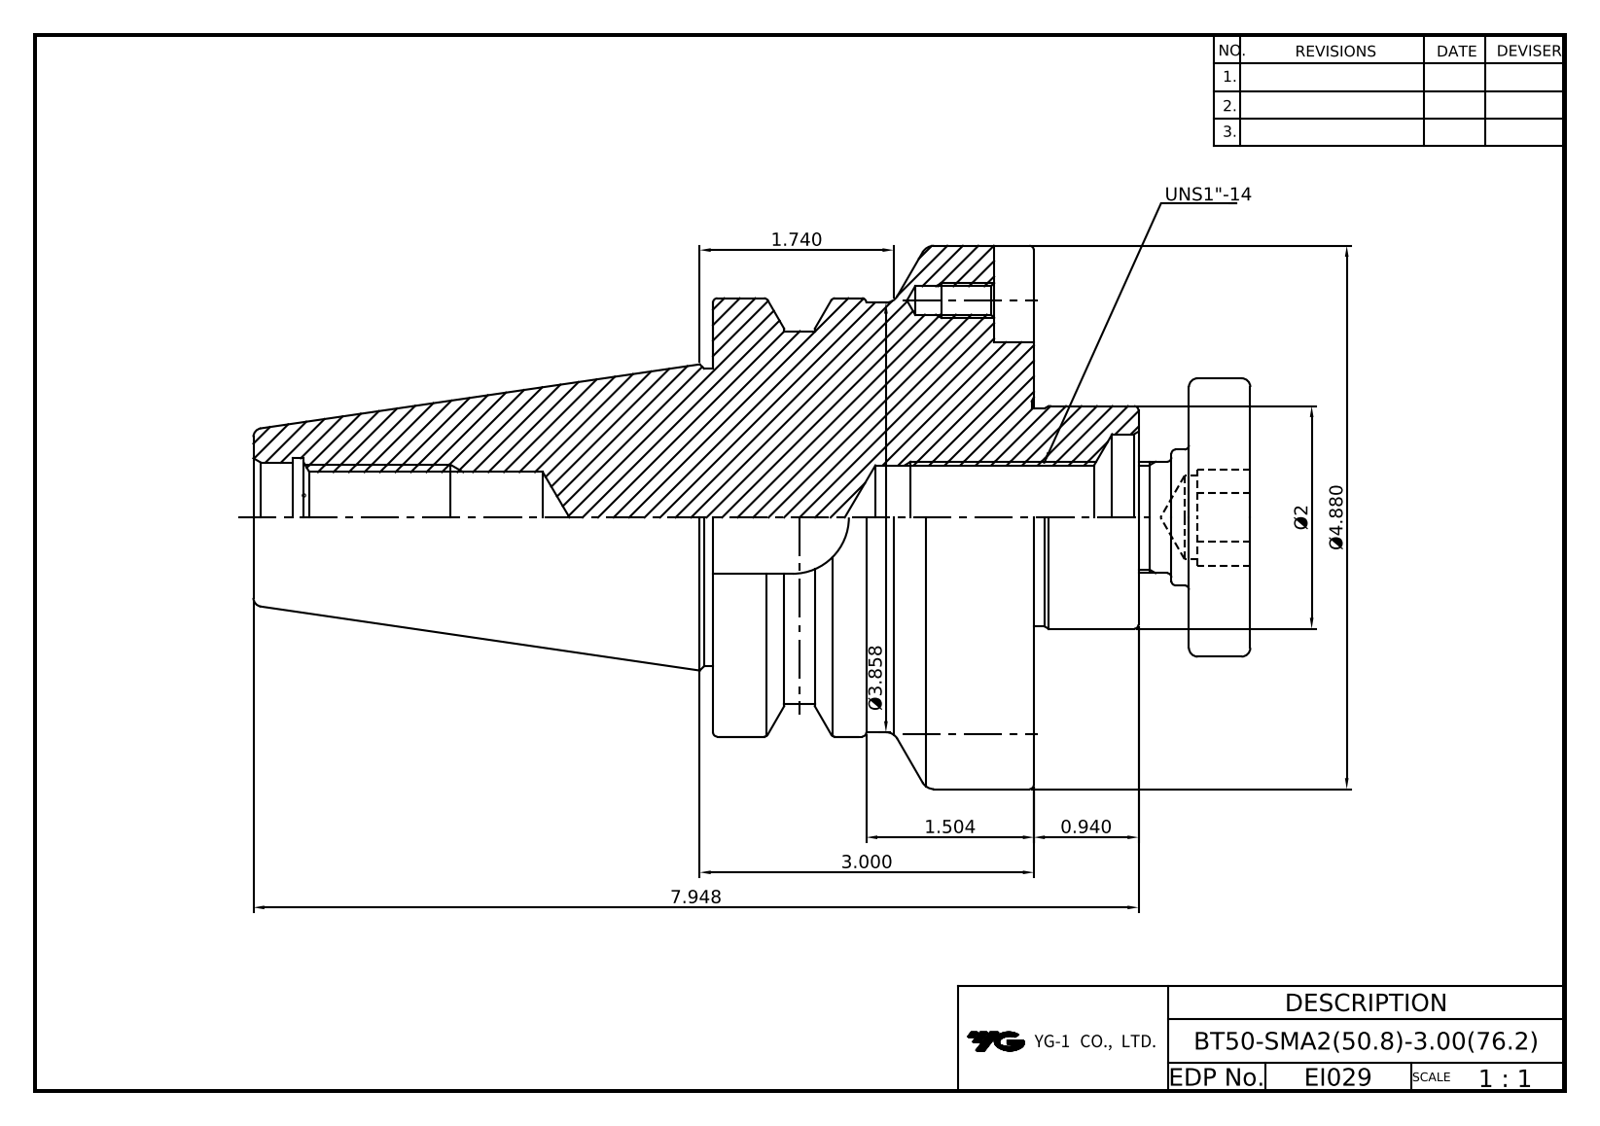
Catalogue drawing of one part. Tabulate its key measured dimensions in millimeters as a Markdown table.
| quantity | value |
| --- | --- |
| part name | LO-BT50-SMA50.8-76.2; DRIVE KEY-19.05.x18x22; HEX'' WRENCH BOLT-UNC5_16-18x3_4L; COLLAR BOLT-UNS1-14x50L |
| STEP written by | Autodesk Inventor 2026 (AUTOMOTIVE_DESIGN) |
| units | millimeters |
| bodies | 6 solids, 142 faces (68 planar, 35 cylindrical, 39 other) |
| overall size | 223.3 × 124 × 124 |
| volume | 948 500 mm³ |
| surface area | 105 500 mm² |
| round holes (diameter × count) | 6.4 × 2, 8.6 × 2, 12.6 × 2, 19.1 × 1, 20.5 × 1, 20.8 × 1, 23.4 × 1, 25 × 1, 25.6 × 1, 38 × 1 |
| round bosses / shafts (diameter × count) | 11.9 × 2, 7.9 × 2, 124 × 1, 100 × 1, 98 × 1, 84.6 × 1, 69.3 × 1, 63.5 × 1 |
| partial cylindrical surfaces (radius × count) | 9.5 × 4, 12.9 × 1 |
| main face-to-face distances | 73.2, 118.5, 45.3, 104.5, 31.3, 14, 64.1, 9.1, 40.4, 54.4 |
| hole center spacings | 49.5, 99 |
